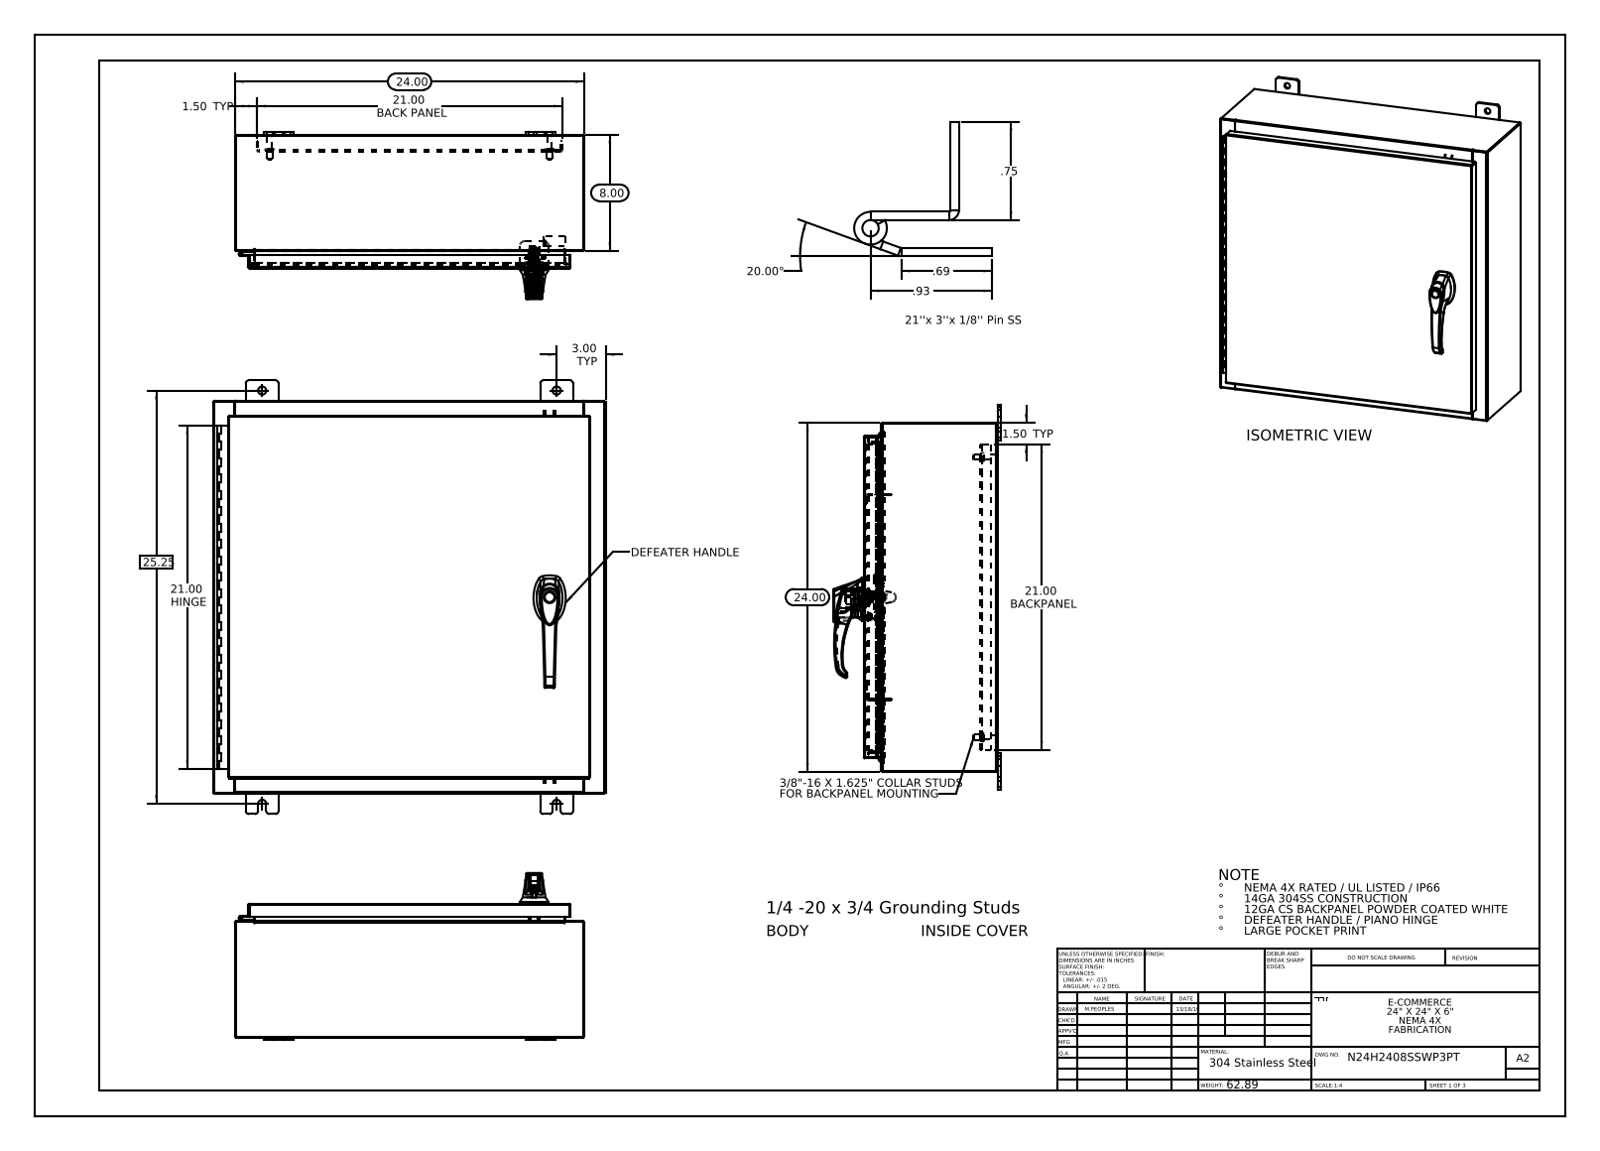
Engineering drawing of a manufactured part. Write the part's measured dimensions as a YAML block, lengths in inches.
part_name: "N24H2408SSWP3PT Body; N24H2408SSWP3PT 263033_Industrilas; 033060_032151; N24H2408SSWP3PT Backpanel (+8 more)"
step_written_by: "SolidWorks 2013 (CONFIG_CONTROL_DESIGN)"
units: inches
bodies: {solids: 31, faces: 2412, planar: 865, cylindrical: 893, other: 654}
overall_size: [26.5, 24, 11.495]
volume: 223.3
surface_area: 5520
round_holes:
  - {diameter: 0.5, count: 8}
  - {diameter: 0.25, count: 4}
  - {diameter: 0.138, count: 3}
  - {diameter: 0.161, count: 3}
  - {diameter: 0.079, count: 2}
  - {diameter: 0.203, count: 2}
  - {diameter: 0.313, count: 2}
  - {diameter: 0.437, count: 2}
  - {diameter: 0.125, count: 1}
  - {diameter: 0.125, count: 1}
  - {diameter: 0.197, count: 1}
  - {diameter: 0.276, count: 1}
round_bosses_or_shafts:
  - {diameter: 0.625, count: 4}
  - {diameter: 0.375, count: 4}
  - {diameter: 0.33, count: 4}
  - {diameter: 1.181, count: 1}
  - {diameter: 0.748, count: 1}
  - {diameter: 0.68, count: 1}
  - {diameter: 0.661, count: 1}
  - {diameter: 0.639, count: 1}
partial_cylinders:
  - {radius: 0.118, count: 37}
  - {radius: 0.006, count: 33}
  - {radius: 0.19, count: 24}
  - {radius: 0.013, count: 22}
  - {radius: 0.088, count: 18}
  - {radius: 0.039, count: 15}
  - {radius: 0.028, count: 12}
  - {radius: 0.008, count: 6}
face_to_face_distances: [0.075, 9.126, 23.925, 9.051, 9.201, 0.104, 1, 1.075, 8.051, 8.126]
hole_center_spacings: [7.68, 0.295, 0.625, 0.841, 1.25, 1.313, 1.561, 1.858]
